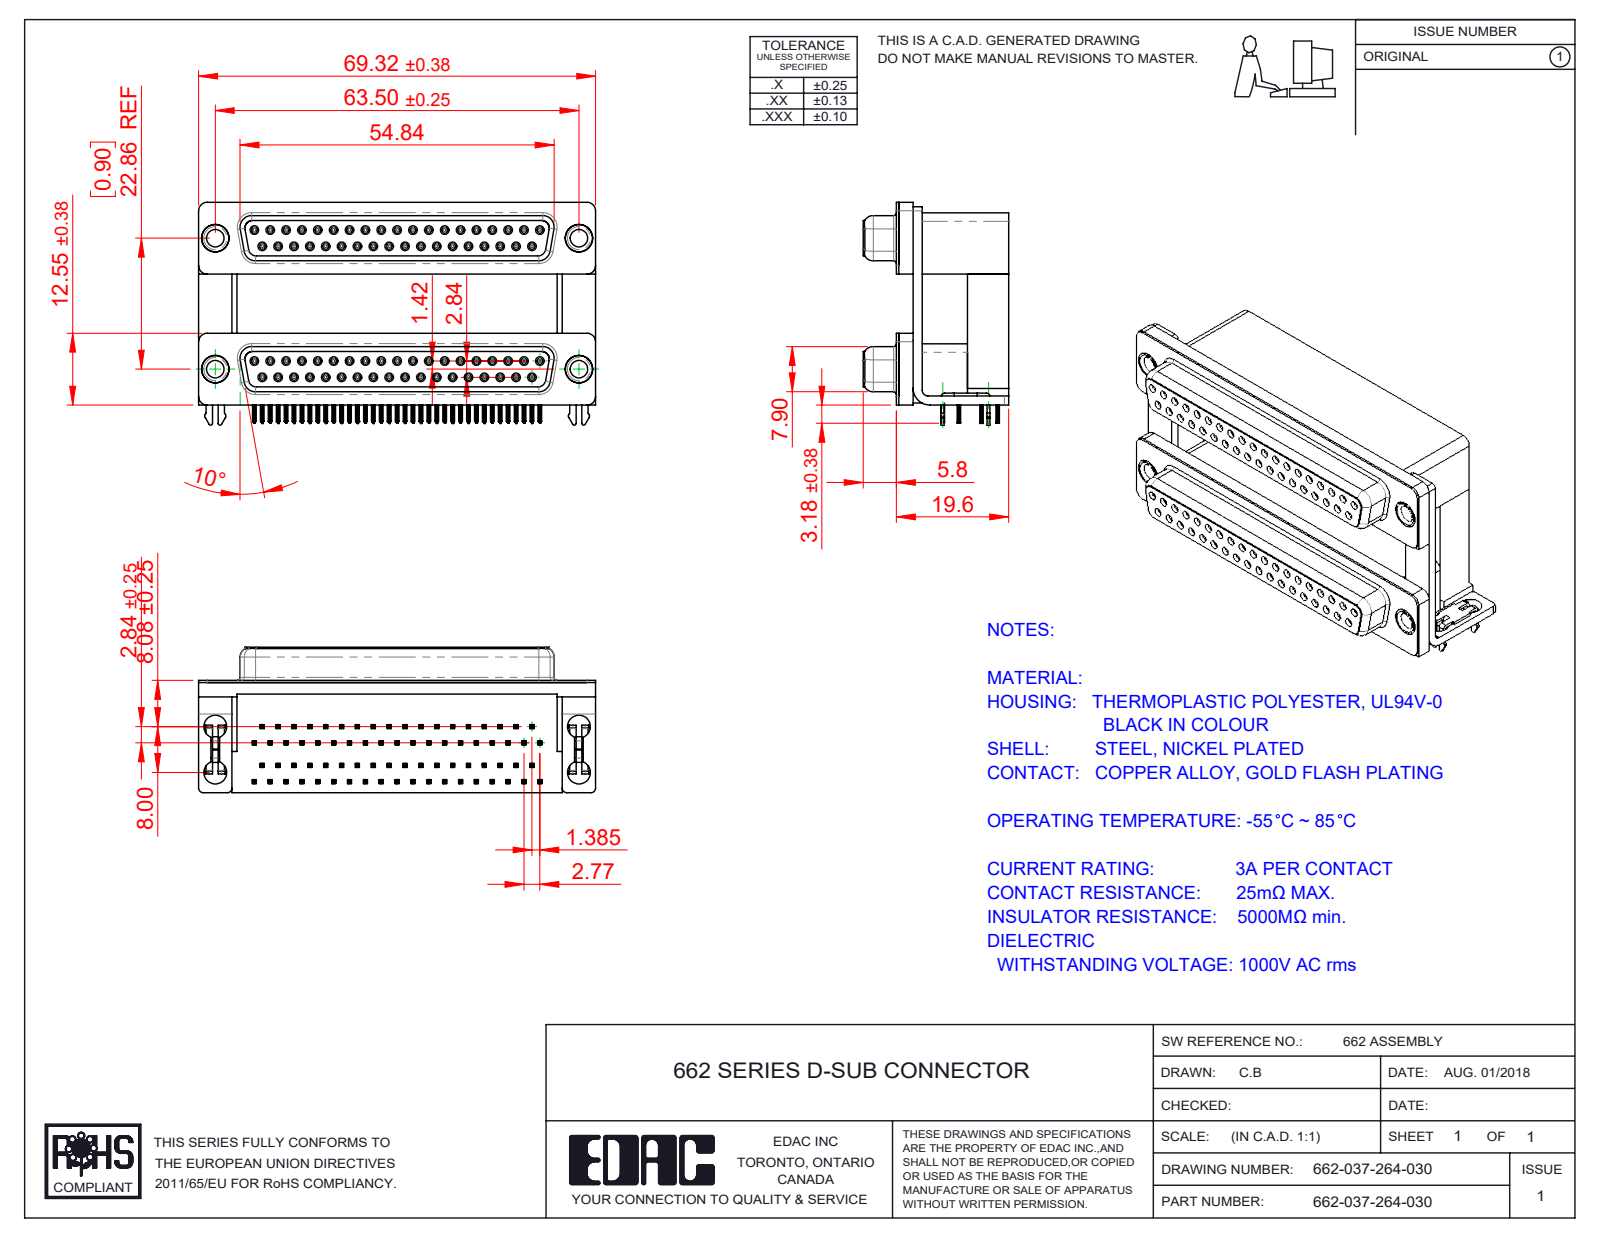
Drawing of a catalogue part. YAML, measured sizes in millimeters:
part_name: "662 Thru Hole Rivet; 662-037-264-030; 662 Housing Upper_37 Contacts H; 662 Housing Lower_37 Contacts (+8 more)"
step_written_by: "SolidWorks 2020 (CONFIG_CONTROL_DESIGN)"
units: millimeters
bodies: {solids: 87, faces: 11376, planar: 5334, cylindrical: 2574, other: 3468}
overall_size: [69.32, 38.91, 25.4]
volume: 34636
surface_area: 36918
round_holes:
  - {diameter: 0.8, count: 74}
  - {diameter: 0.9, count: 74}
  - {diameter: 4, count: 8}
  - {diameter: 3.05, count: 4}
  - {diameter: 3.5, count: 4}
  - {diameter: 4.8, count: 4}
  - {diameter: 5, count: 4}
round_bosses_or_shafts:
  - {diameter: 1.2, count: 74}
  - {diameter: 4.9, count: 4}
  - {diameter: 4.75, count: 4}
  - {diameter: 3.85, count: 4}
partial_cylinders:
  - {radius: 0.1, count: 594}
  - {radius: 0.15, count: 296}
  - {radius: 0.35, count: 148}
  - {radius: 0.34, count: 74}
  - {radius: 0.28, count: 36}
  - {radius: 1.35, count: 16}
  - {radius: 1.5, count: 13}
  - {radius: 0.5, count: 12}
face_to_face_distances: [19.2, 22.86, 0.4, 7.2, 12, 2.84, 6.2, 0.65, 22.5, 33.2]
hole_center_spacings: [3.16, 2.77, 5.54, 8.31, 11.08, 22.16, 13.85, 19.39]
